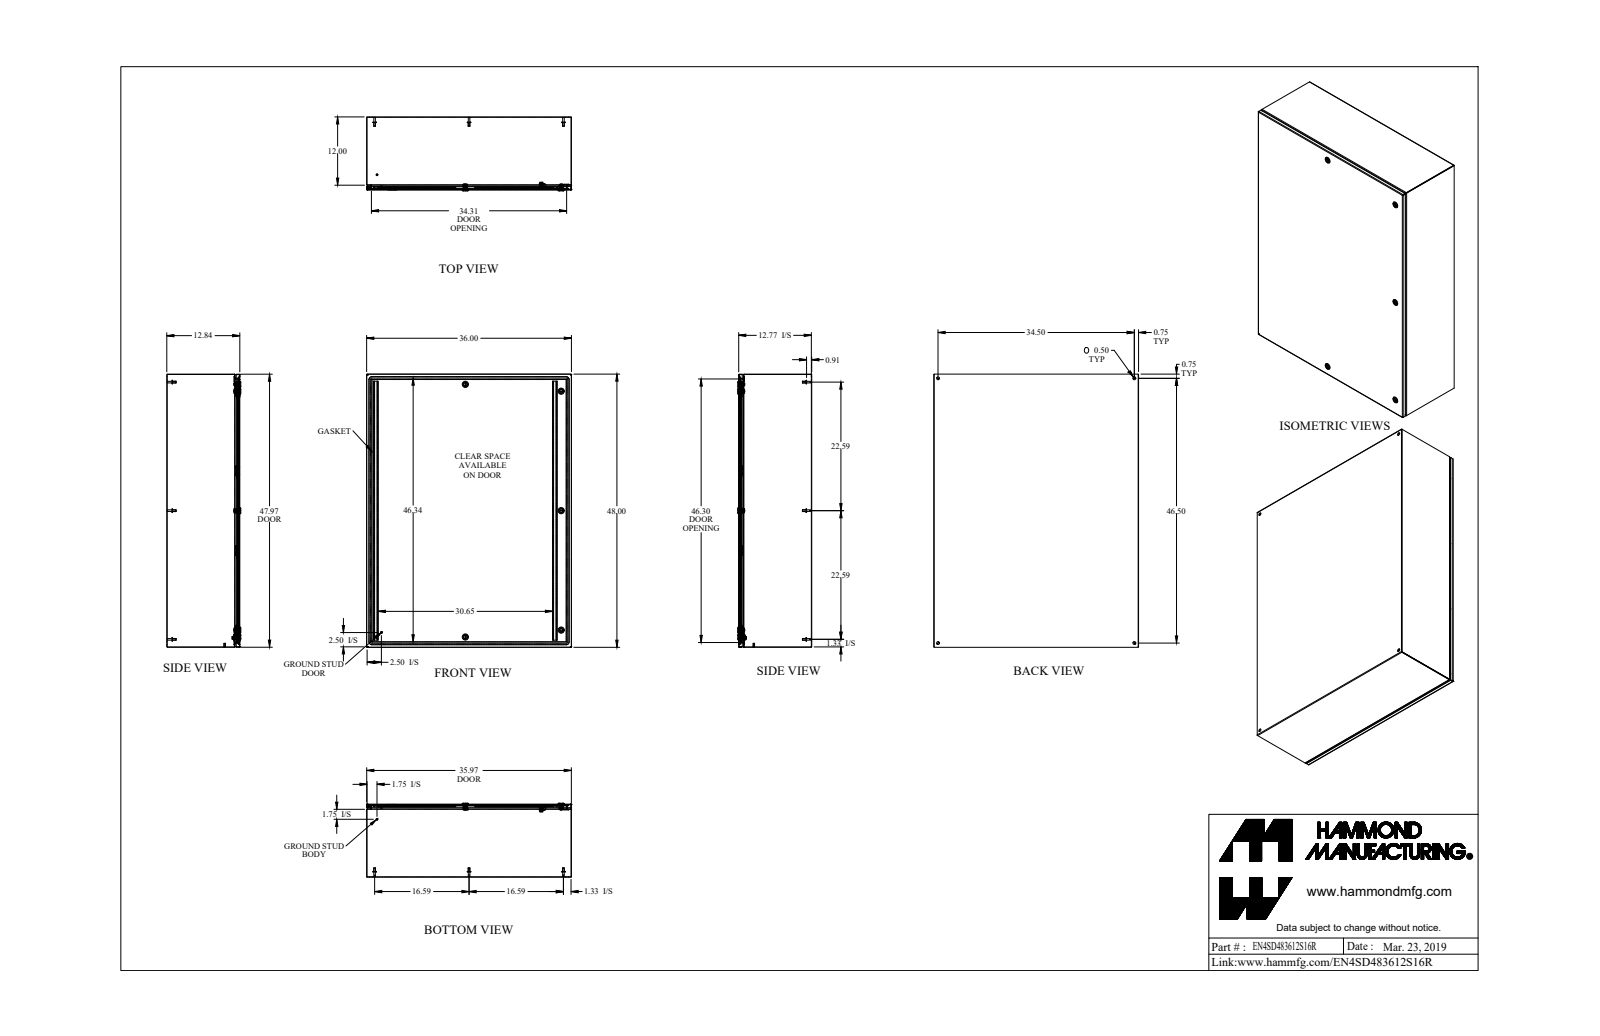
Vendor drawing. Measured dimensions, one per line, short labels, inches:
name: EN4SD483612S16R
written by: SolidWorks 2018 (AUTOMOTIVE_DESIGN)
unit: in
bodies: 65 solids, 1684 faces (858 planar, 549 cylindrical, 277 other)
size: 48 × 36 × 13.002
volume: 467.5 in³; area: 12 599 in²
holes: 9× ⌀0.5, 5× ⌀0.197, 5× ⌀0.387, 5× ⌀0.63, 5× ⌀0.768, 1× ⌀0.172, 1× ⌀0.196, 1× ⌀0.24, 1× ⌀0.242, 1× ⌀0.275, 1× ⌀0.375
bosses: 11× ⌀0.625, 10× ⌀0.313, 8× ⌀0.275, 5× ⌀1.1, 5× ⌀0.236, 3× ⌀0.785, 3× ⌀0.625, 3× ⌀0.525
rounds: 24× R0.01, 24× R0.048, 19× R0.036, 19× R0.108, 17× R0.062, 12× R0.25, 10× R0.094, 10× R0.125
face distances: 0.072, 12.77, 12.698, 12.842, 35.928, 35.856, 36, 0.072, 47.928, 47.856
hole spacings: 16.881, 27.854, 34.5, 46.5, 57.901, 2.488, 2.516, 3.767
